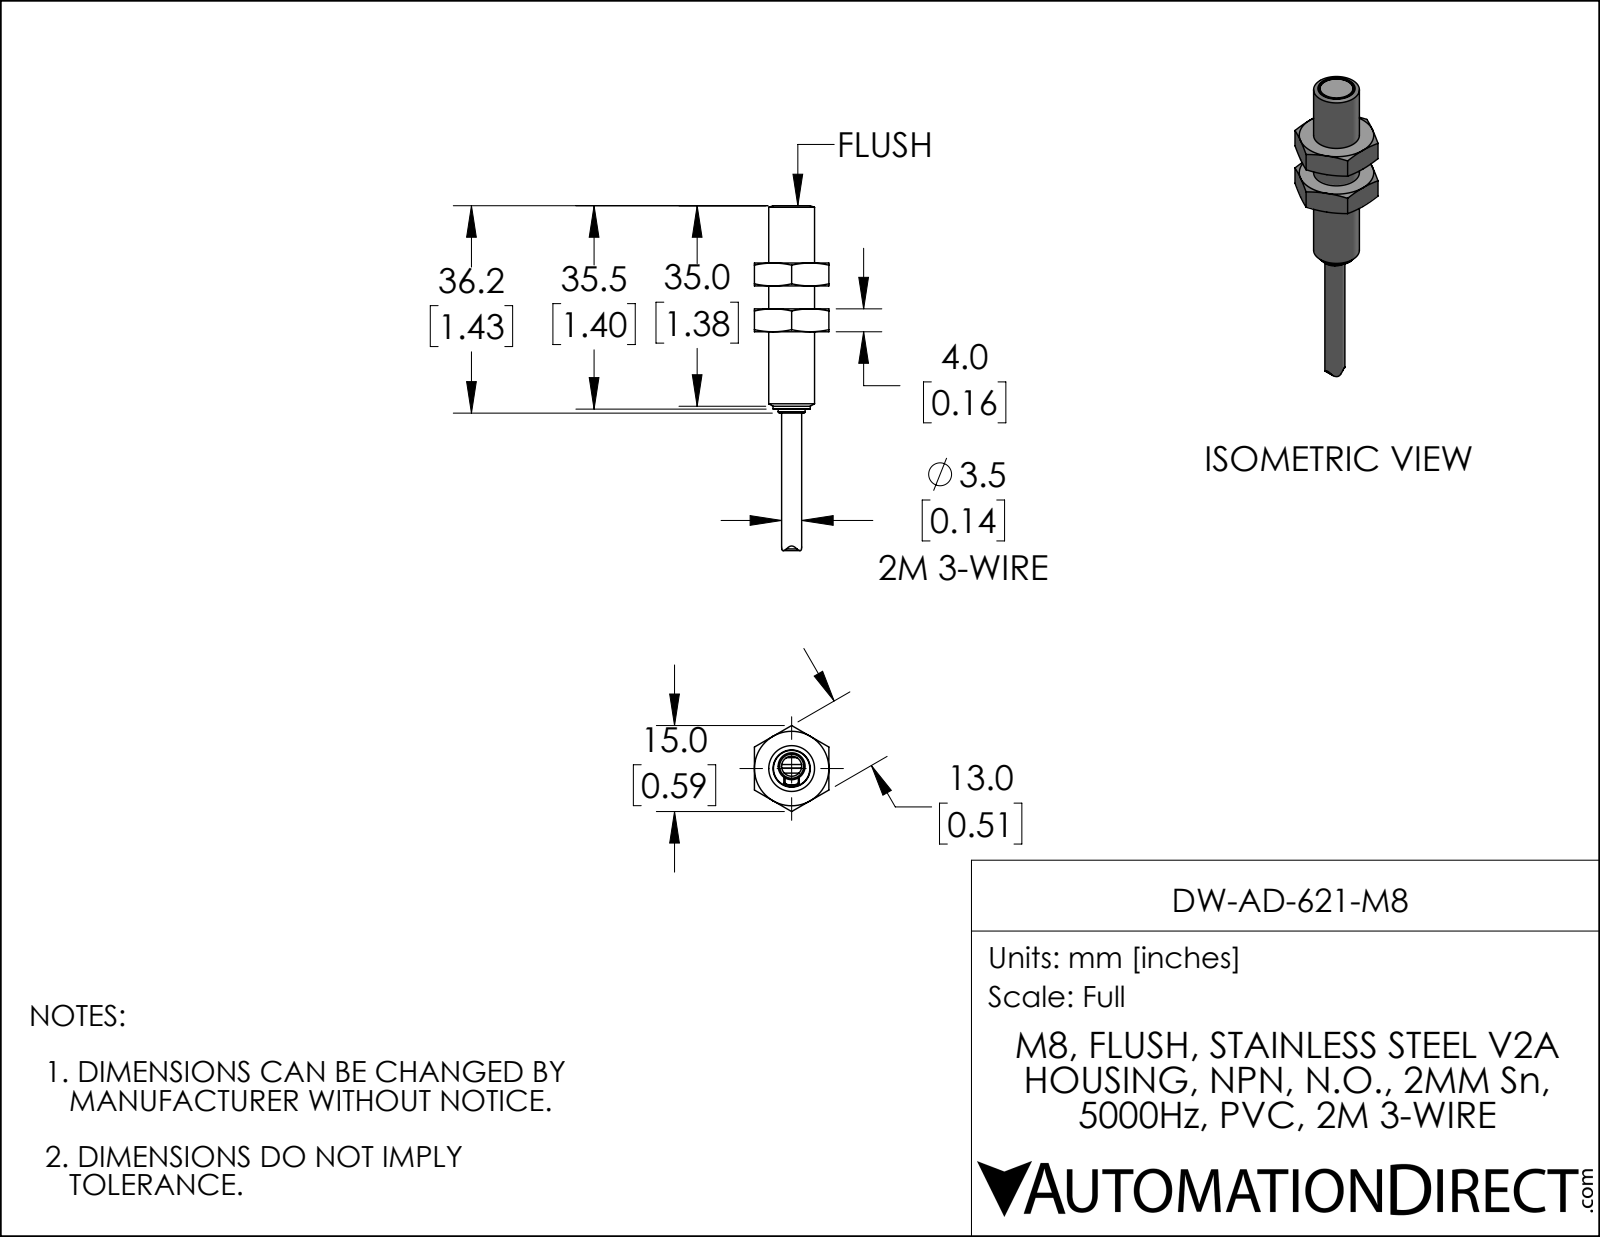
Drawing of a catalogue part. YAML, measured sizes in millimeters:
part_name: "DW-AD-621-M8"
step_written_by: "SolidWorks 2019 (AUTOMOTIVE_DESIGN)"
units: millimeters
bodies: {solids: 1, faces: 79, planar: 24, cylindrical: 18, other: 37}
overall_size: [60.2, 15, 13]
volume: 2770
surface_area: 1773
round_bosses_or_shafts:
  - {diameter: 8, count: 1}
  - {diameter: 6.5, count: 1}
  - {diameter: 4.7, count: 1}
  - {diameter: 3.5, count: 1}
partial_cylinders:
  - {radius: 0.3, count: 2}
  - {radius: 0.6, count: 1}
  - {radius: 0.8, count: 1}
  - {radius: 2.9, count: 1}
  - {radius: 3, count: 1}
  - {radius: 4.5, count: 1}
  - {radius: 6, count: 1}
face_to_face_distances: [4, 13, 8, 12, 10, 14, 18, 22, 35.5, 25.5]
